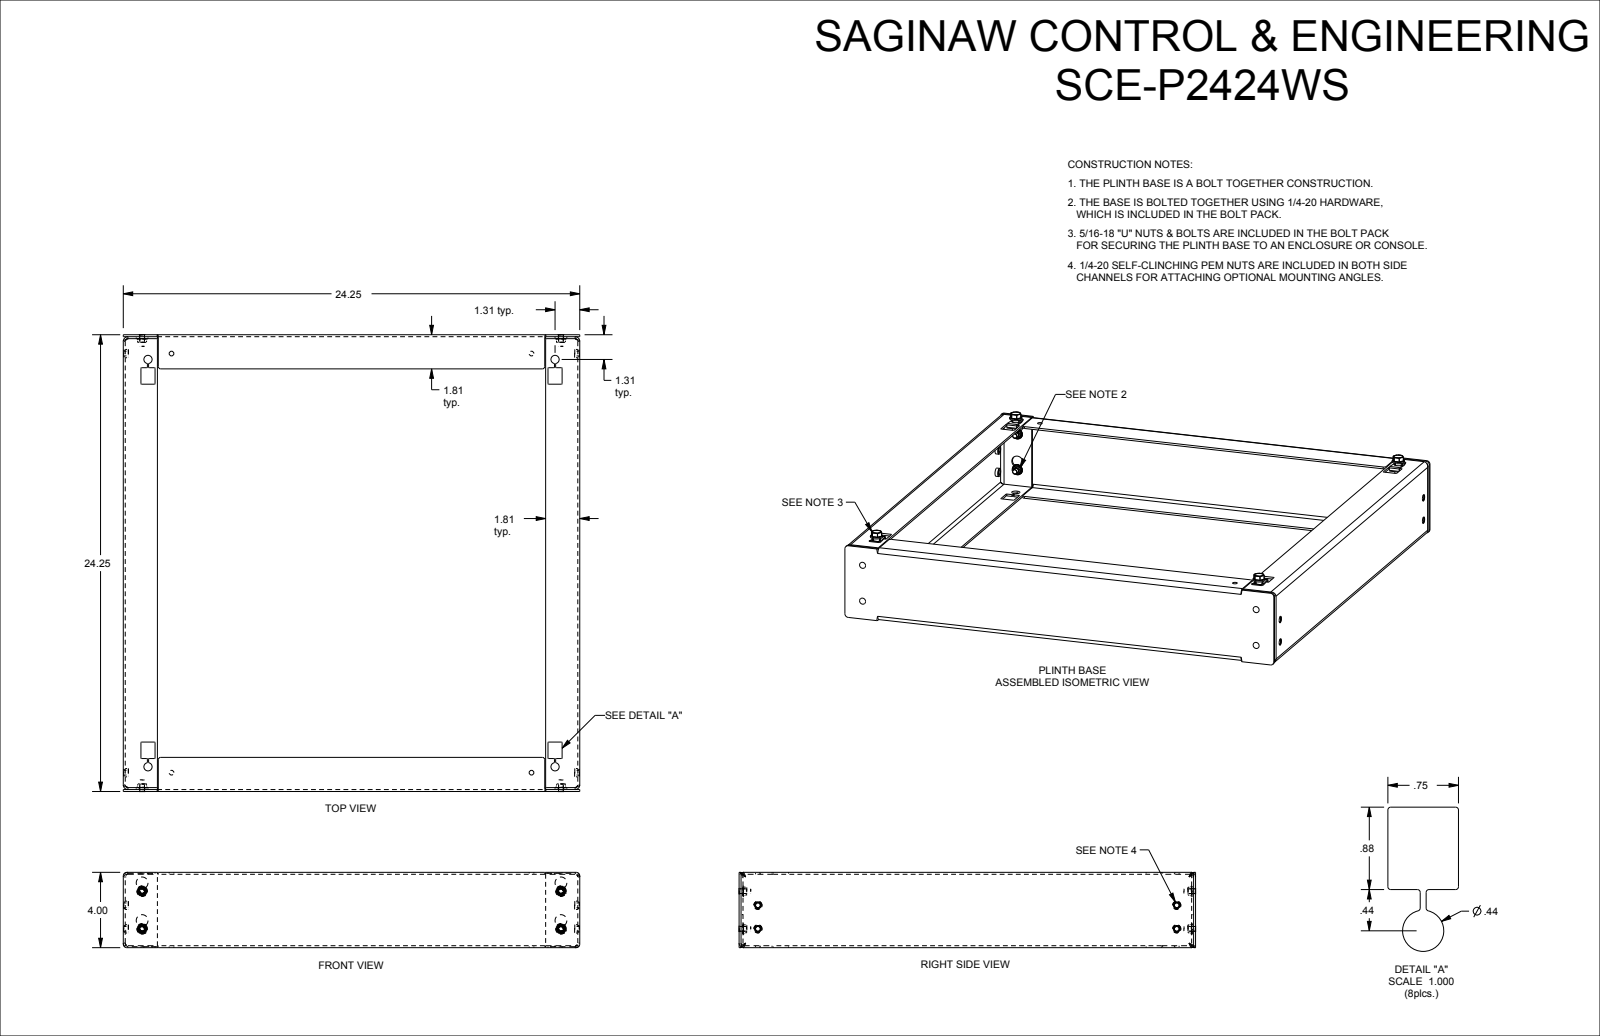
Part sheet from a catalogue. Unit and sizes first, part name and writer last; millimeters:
Units: millimetres
Overall size (bounding box): 616.2 × 616 × 114.6
Round holes (diameter × count): ⌀6.4 ×12, ⌀6.4 ×4, ⌀8.1 ×4, ⌀8.7 ×4, ⌀11.1 ×4, ⌀15.9 ×4
Round bosses / shafts (diameter × count): ⌀14.3 ×4, ⌀11.2 ×4, ⌀9.4 ×4, ⌀8.7 ×4, ⌀8.6 ×4, ⌀7.9 ×4, ⌀6.3 ×4
Partial cylindrical surfaces — rounded edges, fillets, slot ends (radius × count): R0.8 ×46, R0.3 ×24, R0.7 ×24, R3.4 ×8, R6 ×8, R12.7 ×8, R25.4 ×8, R1.5 ×6
Main face-to-face distances: 2.6, 99, 613.3, 613.3, 101.6, 96.3, 610.7, 616, 616, 610.7
Hole centre spacings: 11.2, 50.8, 558.1, 565.2, 565.2, 565.3, 567.4, 31.8
Volume: 1 198 000 mm³ · Surface area: 935 500 mm²
Bodies: 36 solids, 2626 faces (870 planar, 364 cylindrical, 1392 other)
Part name (STEP PRODUCT): SCE-P2424WS
STEP written by: SolidWorks 2021 (AUTOMOTIVE_DESIGN)
